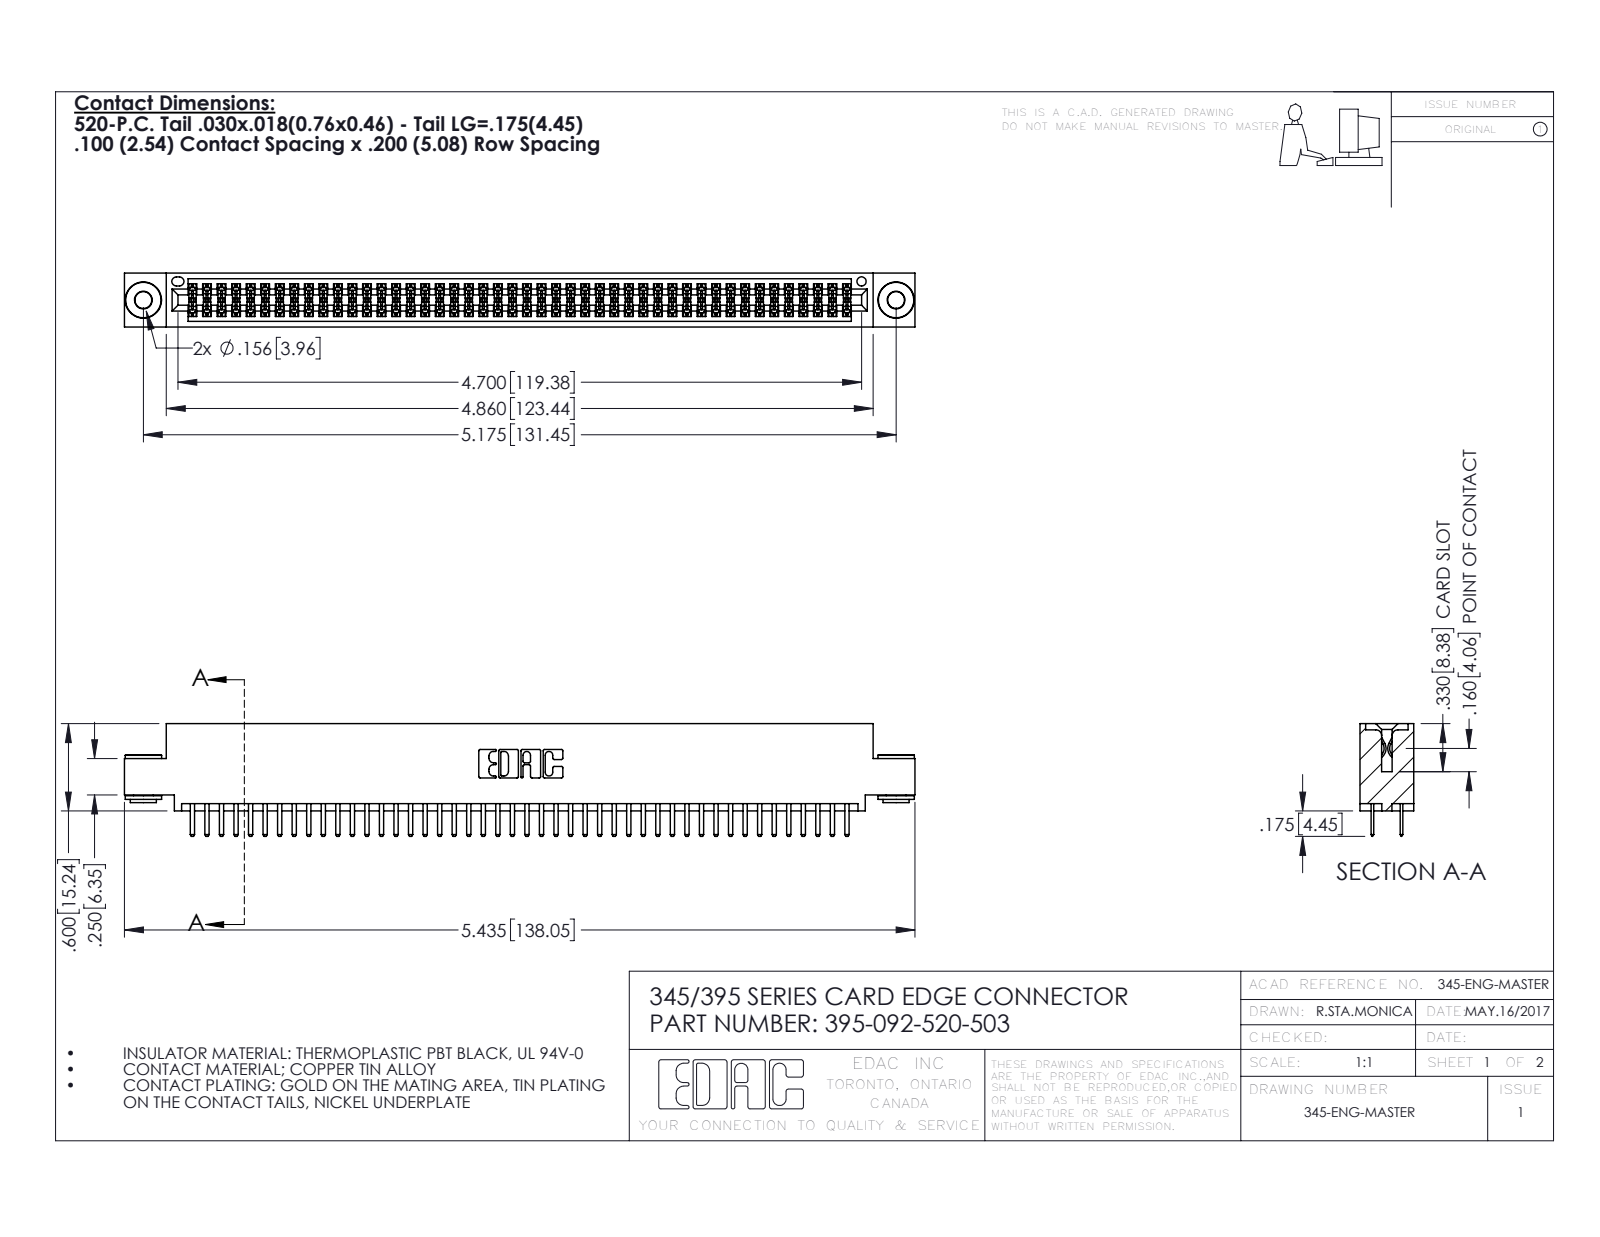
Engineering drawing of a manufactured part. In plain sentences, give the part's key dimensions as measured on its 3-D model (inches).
The part is named "395-092-520-503; 345 Part_0.110 Offset - 0.156 Dia-TH; 345-250-002_345-250-002-102; 345-292-001_345-293-120". Its 3-D file was written by "SolidWorks 2016 (CONFIG_CONTROL_DESIGN)". It is 95 solids with 5136 faces: 3314 planar, 1814 cylindrical and 8 other. Overall it measures 5.435 by 0.775 by 0.37 inches. Its volume is 0.815 cubic inches and its surface area 31.04 square inches. Round holes: 2 of diameter 0.116, 2 of diameter 0.156, 1 of diameter 0.064. Round bosses or shafts: 2 of diameter 0.25, 2 of diameter 0.18, 2 of diameter 0.136. Partial cylindrical surfaces (rounded edges, fillets, slot ends): 138 of radius 0.006, 96 of radius 0.01, 22 of radius 0.01, 6 of radius 0.007, 6 of radius 0.031, 3 of radius 0.026, 2 of radius 0.014, 2 of radius 0.019. The main face-to-face distances are 0.072, 0.298, 0.2, 0.37, 0.025, 0.098, 0.272, 0.225, 0.022, 0.072. The hole center spacings are 0.27, 4.939, 5.175.
